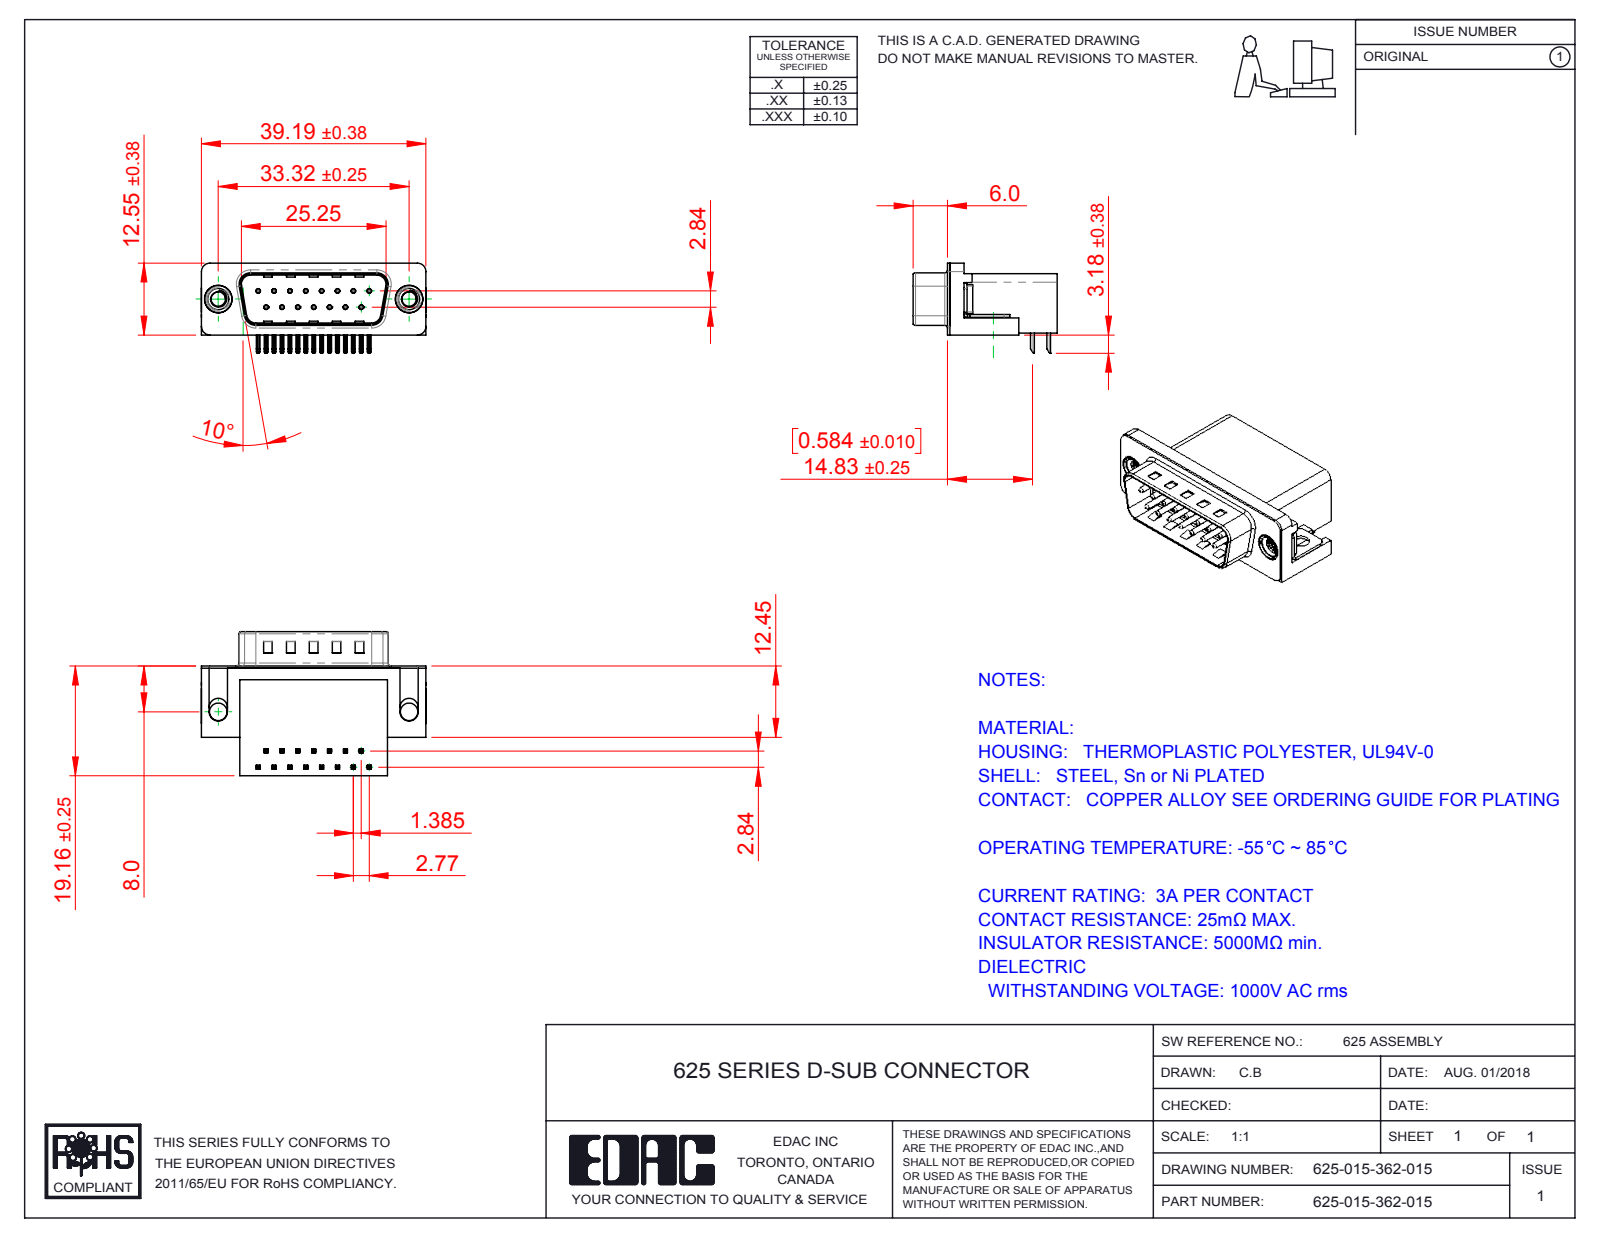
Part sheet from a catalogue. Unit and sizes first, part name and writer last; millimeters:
Units: millimetres
Overall size (bounding box): 39.22 × 25.16 × 15.73
Round holes (diameter × count): ⌀0.35 ×15, ⌀0.8 ×15, ⌀2.5 ×2, ⌀3.05 ×2, ⌀4 ×2, ⌀4.8 ×2, ⌀5 ×2
Round bosses / shafts (diameter × count): ⌀0.75 ×15, ⌀4.9 ×2, ⌀4.75 ×2, ⌀3.9 ×2
Partial cylindrical surfaces — rounded edges, fillets, slot ends (radius × count): R0.25 ×68, R0.12 ×30, R1 ×16, R0.5 ×9, R1.6 ×8, R1.5 ×6, R0.9 ×4, R2 ×4
Main face-to-face distances: 0.4, 10.35, 18.76, 2.1, 10.46, 19.16, 1.7, 10.86, 8.76, 16.26
Hole centre spacings: 3.16, 2.77, 5.54, 8.31, 11.08, 5.03, 5.04, 7.48
Volume: 6 235 mm³ · Surface area: 6 415 mm²
Bodies: 21 solids, 1479 faces (893 planar, 451 cylindrical, 135 other)
Part name (STEP PRODUCT): 625 Shell_15 Socket; 625 Contact Bottom; 625 Housing_15 Socket; 625 Contact Top (+3 more)
STEP written by: SolidWorks 2016 (CONFIG_CONTROL_DESIGN)
